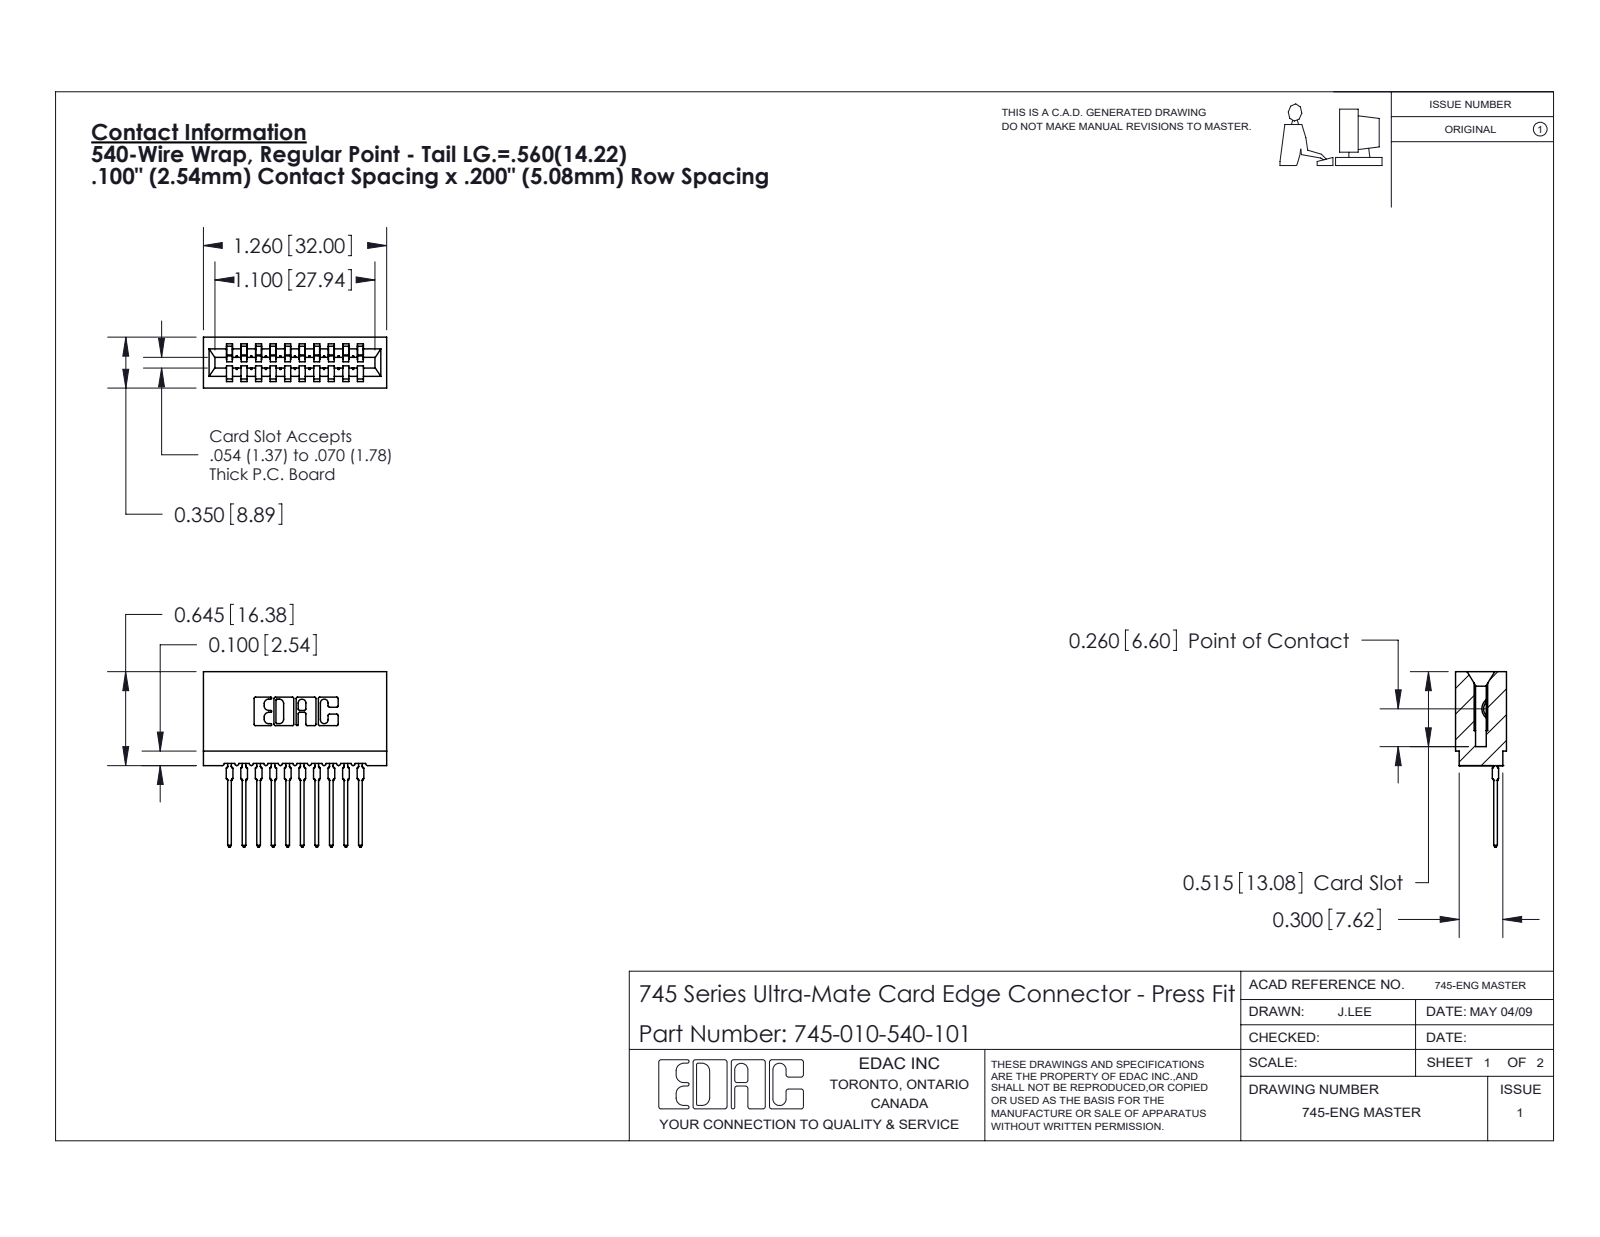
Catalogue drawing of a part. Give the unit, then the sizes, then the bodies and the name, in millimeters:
Units: millimetres
Overall size (bounding box): 32 × 30.6 × 8.9
Partial cylindrical surfaces — rounded edges, fillets, slot ends (radius × count): R0.3 ×22, R0.4 ×20, R0.5 ×20, R0.2 ×6, R0.8 ×6, R0.1 ×4, R0.3 ×4, R0.7 ×3
Main face-to-face distances: 2.5, 5.1, 7.6, 10.2, 12.7, 4, 1.5, 1.1, 6.6, 3.6
Volume: 3 020 mm³ · Surface area: 5 082 mm²
Bodies: 11 solids, 1215 faces (725 planar, 230 cylindrical, 260 other)
Part name (STEP PRODUCT): 745 Part_Insulator Option - 01; 745-010-540-101; 745-292-001_540
STEP written by: SolidWorks 2020 (CONFIG_CONTROL_DESIGN)
